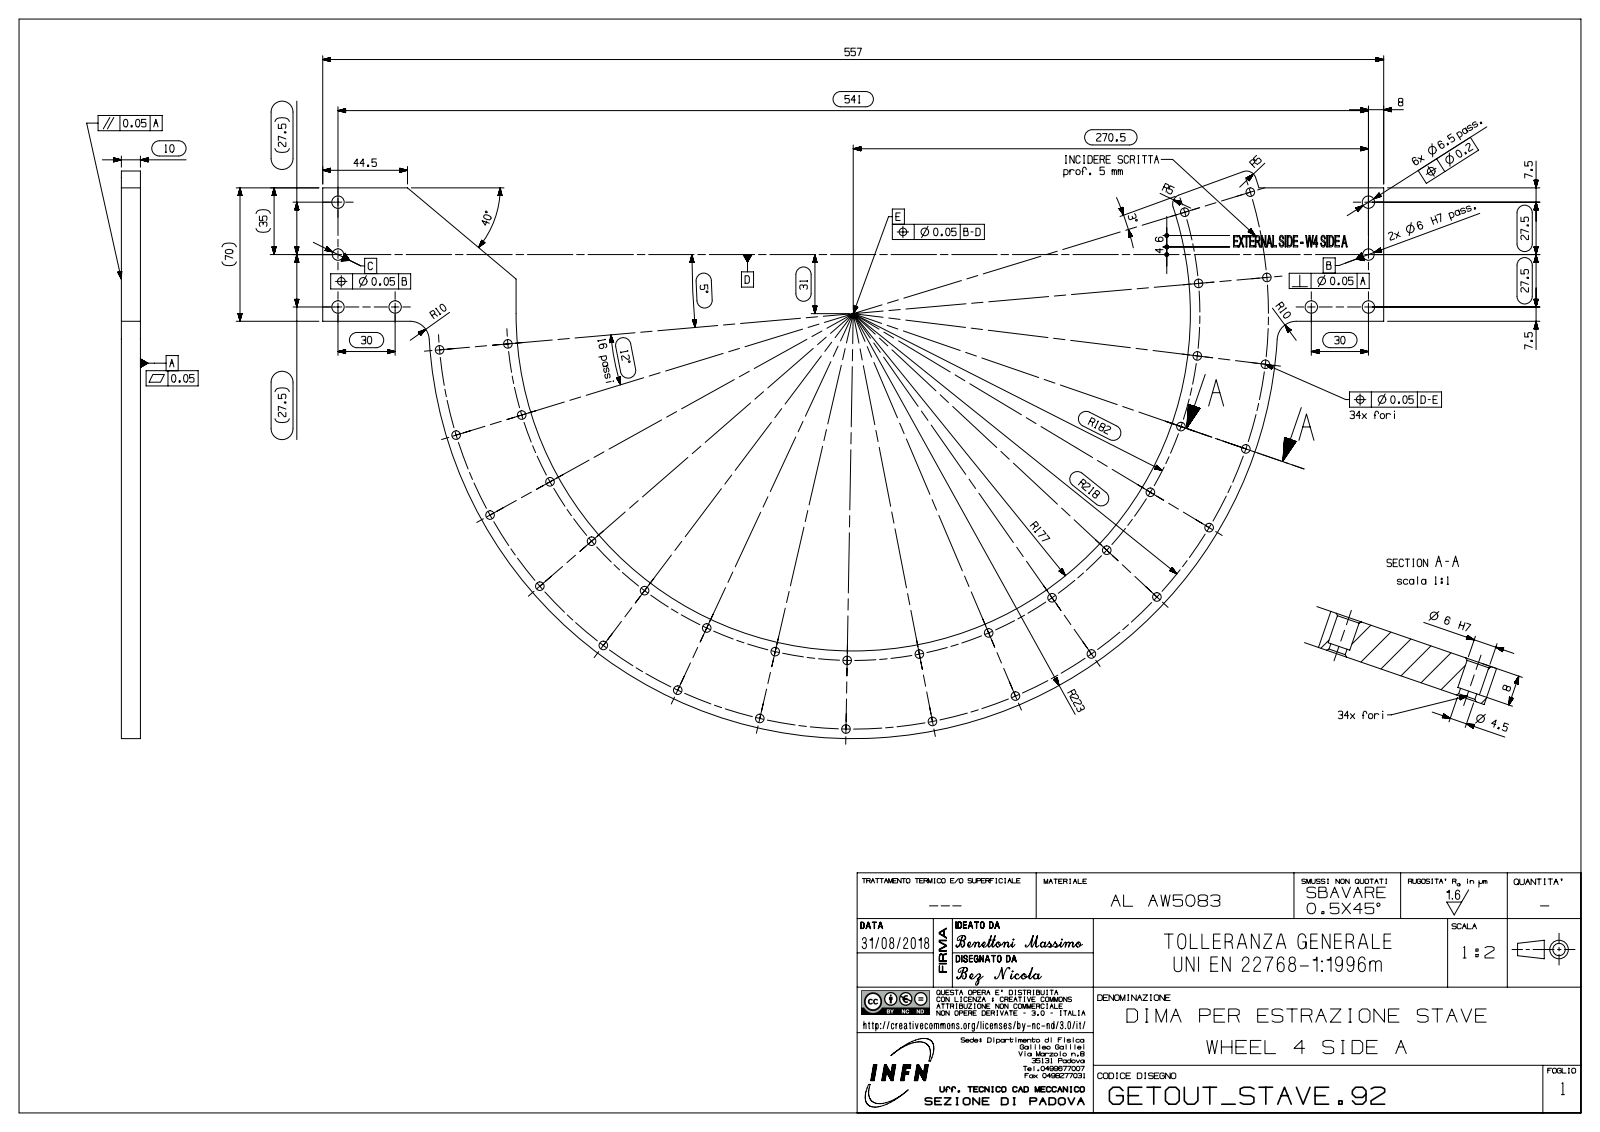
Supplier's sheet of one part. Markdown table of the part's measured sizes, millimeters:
| quantity | value |
| --- | --- |
| part name | bez8324385A6uxt |
| STEP written by | SIEMENS PLM Software NX 12.0 (AUTOMOTIVE_DESIGN) |
| units | millimeters |
| bodies | 1 solid, 418 faces (219 planar, 83 cylindrical, 116 other) |
| overall size | 557 × 297.84 × 10 |
| volume | 406 455 mm³ |
| surface area | 107 626 mm² |
| round holes (diameter × count) | 6 × 36, 4.5 × 34, 6.5 × 6 |
| partial cylindrical surfaces (radius × count) | 5 × 2, 10 × 2, 177 × 1, 223 × 1 |
| main face-to-face distances | 10, 70, 557, 8, 2, 455.5, 101.5, 9.5, 1.5, 0.5 |
| hole center spacings | 128.26, 55.05, 90.31, 165.99, 202.42, 55.04, 236.91, 268.99 |
